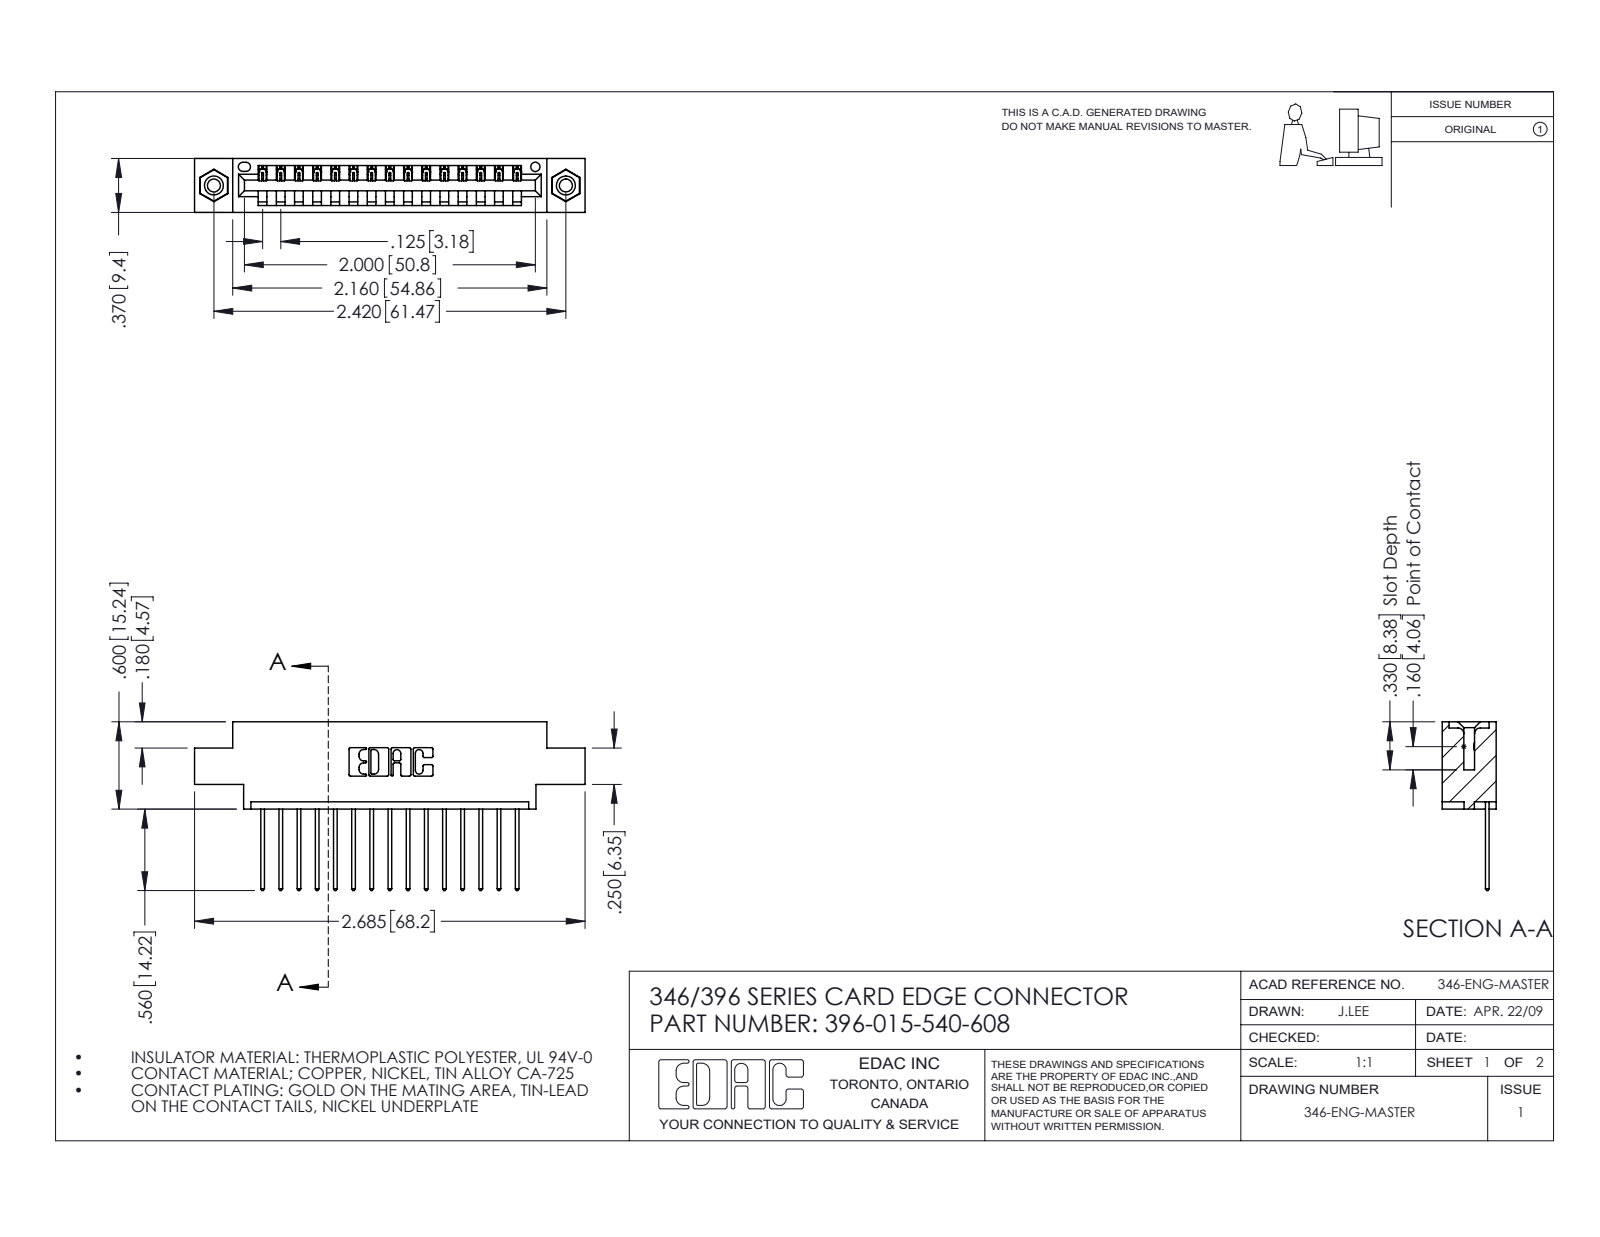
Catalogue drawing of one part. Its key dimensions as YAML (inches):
part_name: "345-250-001_345-250-003-102; 346 Part_0.170 Offset - 0.156 Dia-TI; 345-292-001_345-293-140; 396-015-540-608"
step_written_by: "SolidWorks 2016 (CONFIG_CONTROL_DESIGN)"
units: inches
bodies: {solids: 18, faces: 1056, planar: 712, cylindrical: 328, other: 16}
overall_size: [2.685, 1.16, 0.37]
volume: 0.378
surface_area: 12.07
round_holes:
  - {diameter: 0.089, count: 2}
  - {diameter: 0.125, count: 2}
  - {diameter: 0.156, count: 2}
  - {diameter: 0.064, count: 1}
round_bosses_or_shafts:
  - {diameter: 0.155, count: 2}
partial_cylinders:
  - {radius: 0.006, count: 30}
  - {radius: 0.01, count: 30}
  - {radius: 0.01, count: 22}
  - {radius: 0.007, count: 6}
  - {radius: 0.031, count: 6}
  - {radius: 0.026, count: 3}
  - {radius: 0.031, count: 2}
  - {radius: 0.04, count: 2}
face_to_face_distances: [0.048, 0.322, 0.37, 0.25, 0.072, 0.298, 0.025, 0.222, 0.148, 0.1]
hole_center_spacings: [0.246, 2.213, 2.42]
